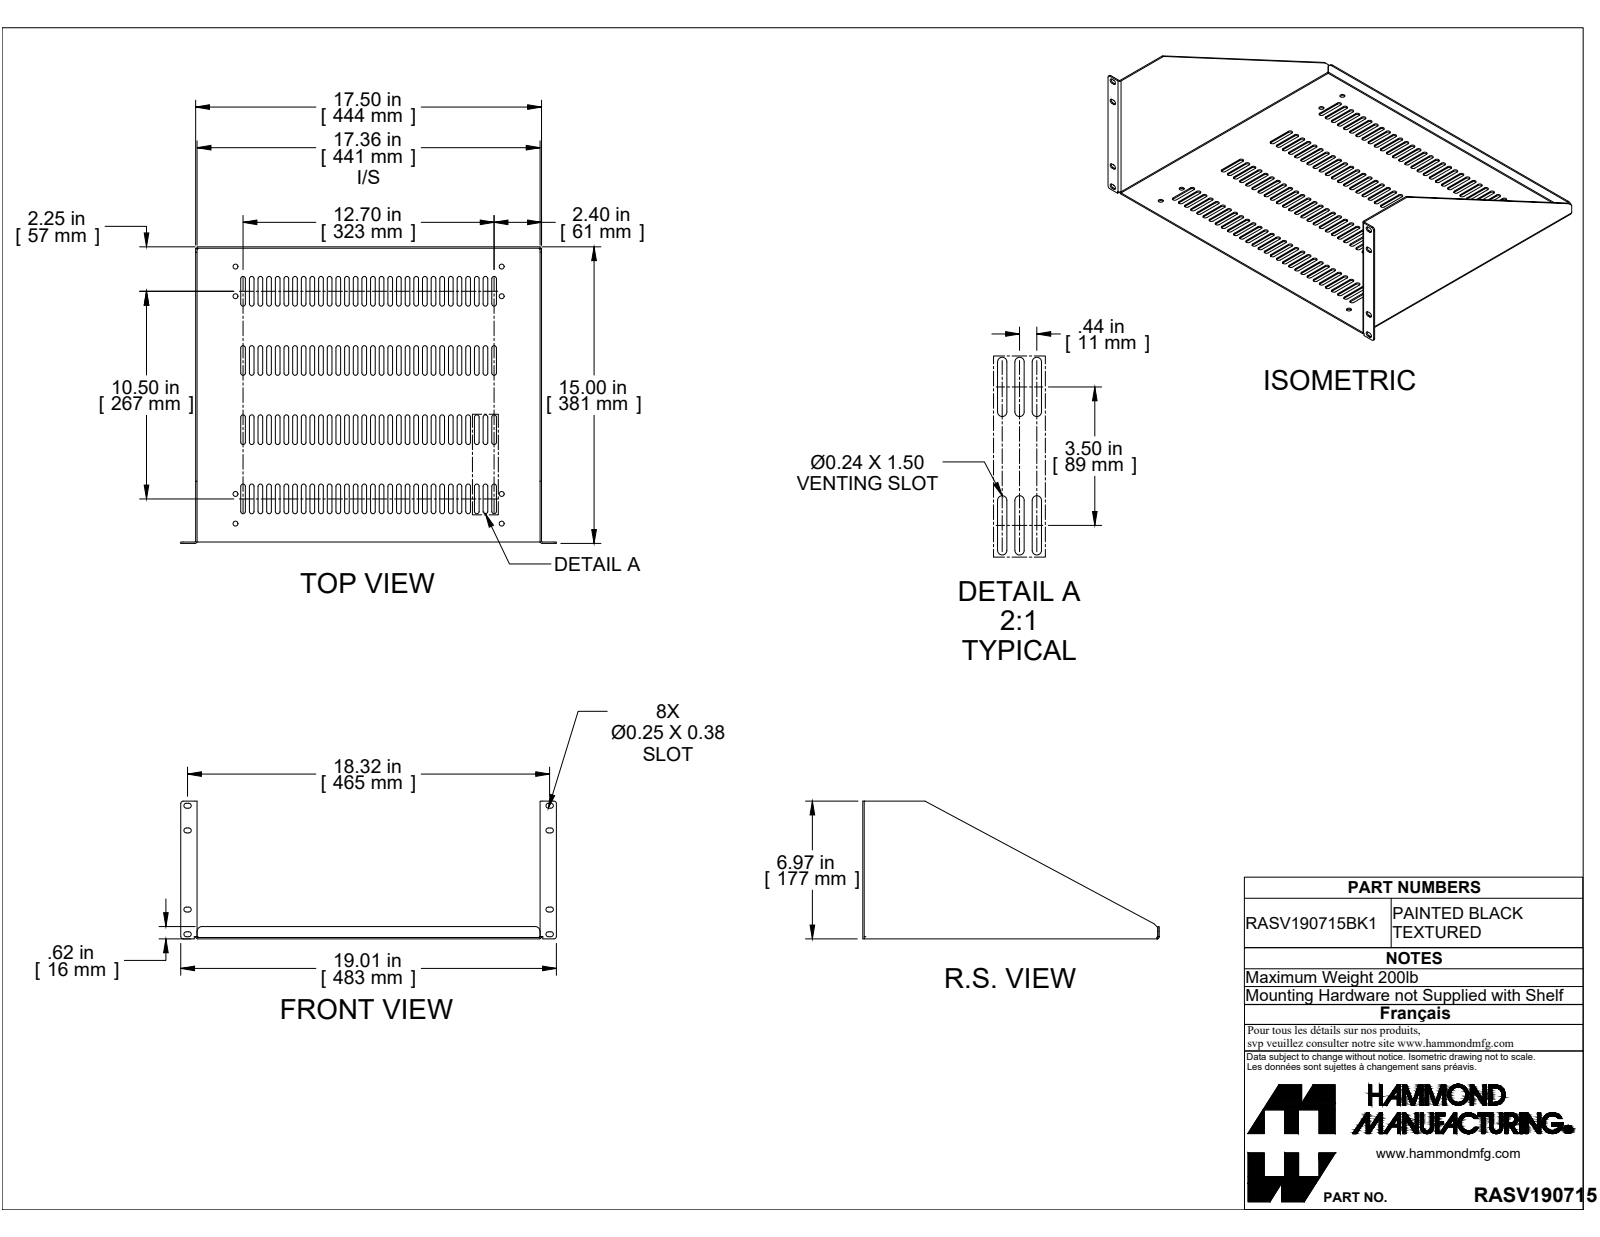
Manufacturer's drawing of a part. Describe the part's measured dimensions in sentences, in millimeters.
The part is named "RASV190715BK1". Its 3-D file was written by "SolidWorks 2019 (CONFIG_CONTROL_DESIGN)". It is 1 solid with 584 faces: 296 planar, 284 cylindrical and 4 other. Overall it measures 482.8 by 381 by 177 millimeters. Its volume is 435 400 cubic millimeters and its surface area 499 200 square millimeters. Round holes: 8 of diameter 6.4. Partial cylindrical surfaces (rounded edges, fillets, slot ends): 232 of radius 3, 20 of radius 3.2, 8 of radius 3, 5 of radius 0.9, 5 of radius 2.7, 3 of radius 1.4, 2 of radius 6.4. The main face-to-face distances are 1.8, 442.7, 440.8, 444.5, 1.8, 381, 379.2, 379.2, 377.3, 22.3. The hole center spacings are 38.1, 292.1, 342.1, 344.2, 449.8, 254, 330.2, 426.1.
